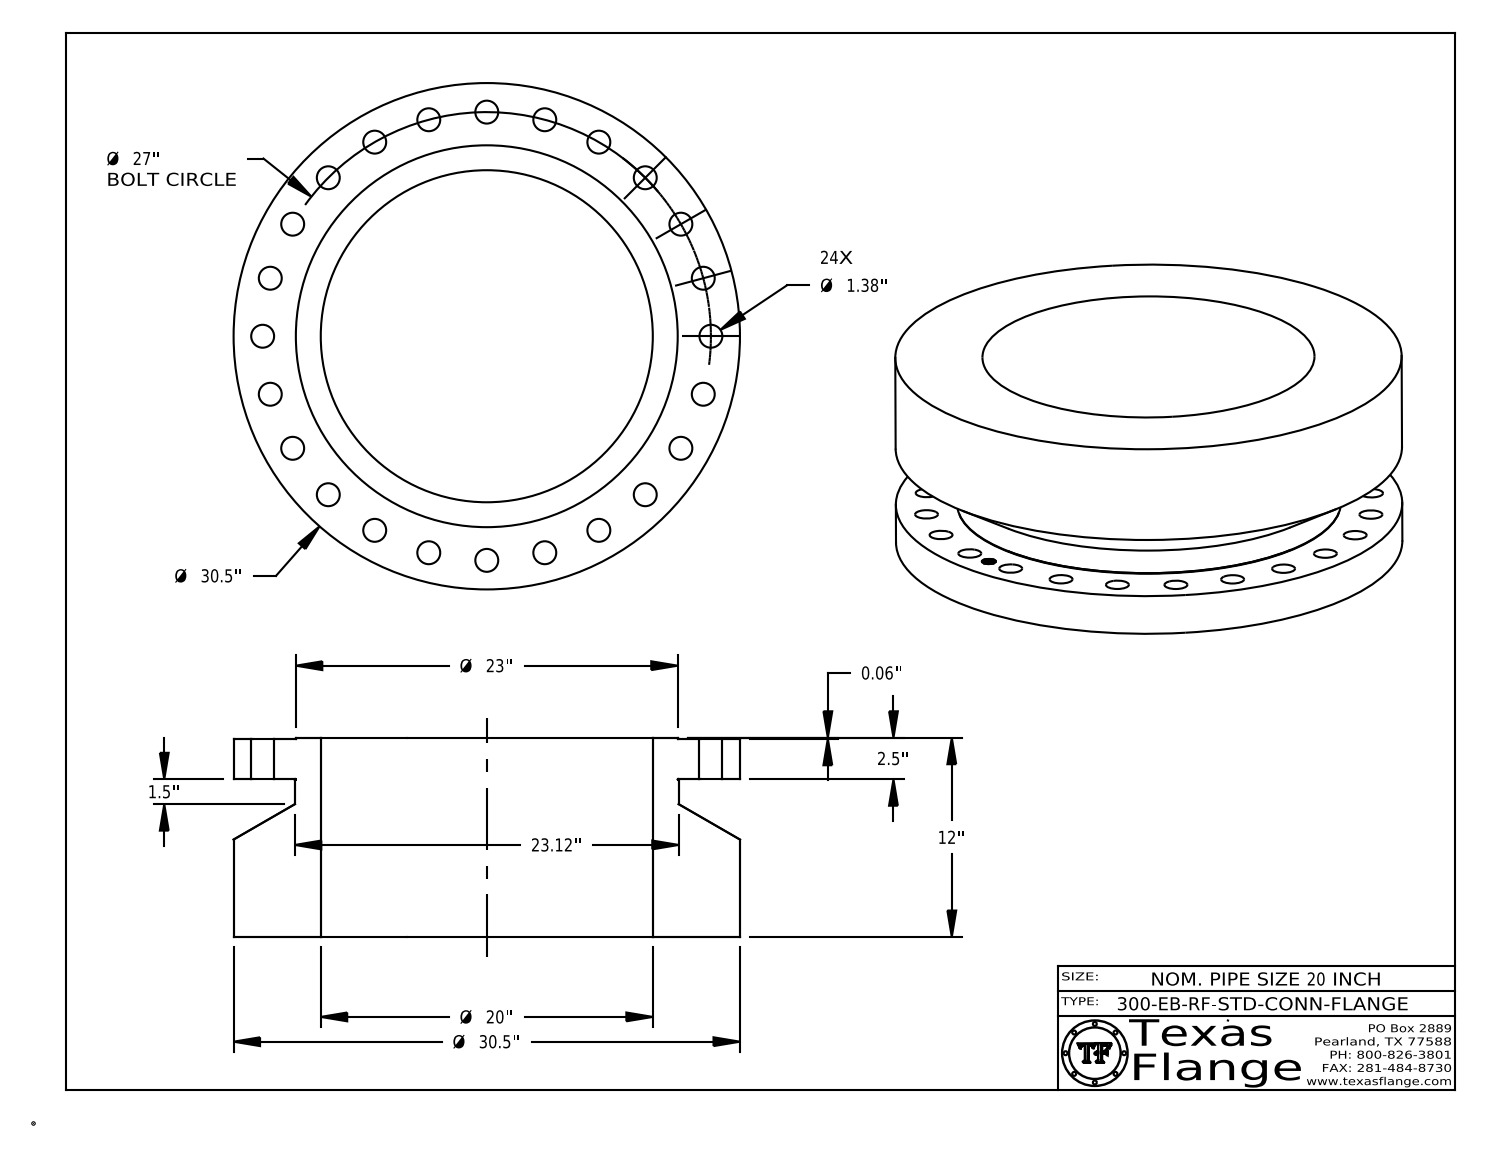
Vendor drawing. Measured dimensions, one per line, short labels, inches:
name: 20-300-EB-RF-STD-CONN-FLANGE
written by: CATIA V5 STEP AP214 (AUTOMOTIVE_DESIGN)
unit: in
bodies: 1 solid, 453 faces (369 planar, 78 cylindrical, 6 other)
size: 30.5 × 30.5 × 12
volume: 4 078 in³; area: 3 351 in²
holes: 24× ⌀1.38, 1× ⌀0.85, 1× ⌀20
bosses: 8× ⌀0.051, 1× ⌀30.5, 1× ⌀23.12, 1× ⌀23, 1× ⌀0.67
face distances: 11.937, 2.437, 9.5, 0.063, 2.5, 12, 2.495, 2.433, 9.505, 0.254
hole spacings: 13.5, 3.524, 6.988, 10.333, 16.437, 24.945, 26.769, 21.421
